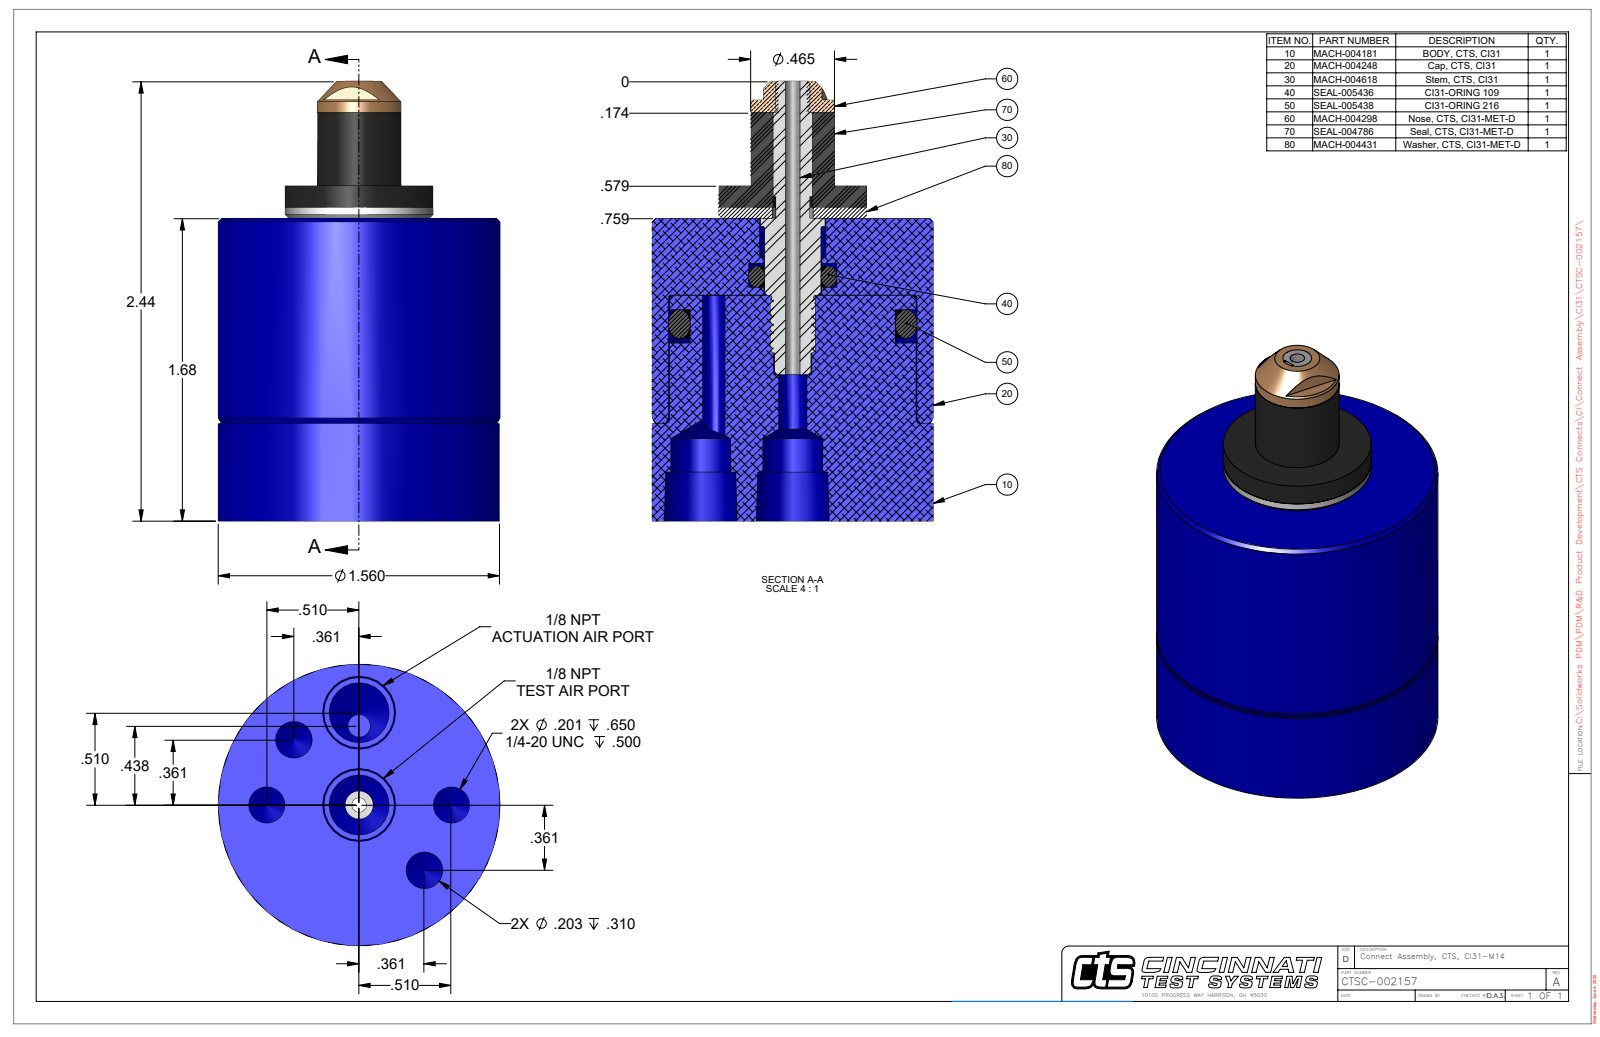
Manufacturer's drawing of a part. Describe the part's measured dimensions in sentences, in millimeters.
The part is named "CTSC-002157". Its 3-D file was written by "SolidWorks 2023 (AUTOMOTIVE_DESIGN)". It is 1 solid with 88 faces: 22 planar, 36 cylindrical and 30 other. Overall it measures 61.9 by 39.6 by 39.6 millimeters. Its volume is 52 320 cubic millimeters and its surface area 12 150 square millimeters. Round holes: 2 of diameter 5.1, 2 of diameter 5.2, 2 of diameter 8.4, 1 of diameter 2.1, 1 of diameter 3.2, 1 of diameter 4, 1 of diameter 9.3, 1 of diameter 35. Round bosses or shafts: 1 of diameter 39.6, 1 of diameter 34.7, 1 of diameter 20.8, 1 of diameter 11.8, 1 of diameter 9.1. Partial cylindrical surfaces (rounded edges, fillets, slot ends): 1 of radius 2. The main face-to-face distances are 42.6, 47.2, 4.6, 13.8, 28.8, 33.4, 20.6, 6.9, 22, 26.5. The hole center spacings are 13, 9.9, 23.9, 17.1, 18.3, 1.8, 9.4, 11.1.
